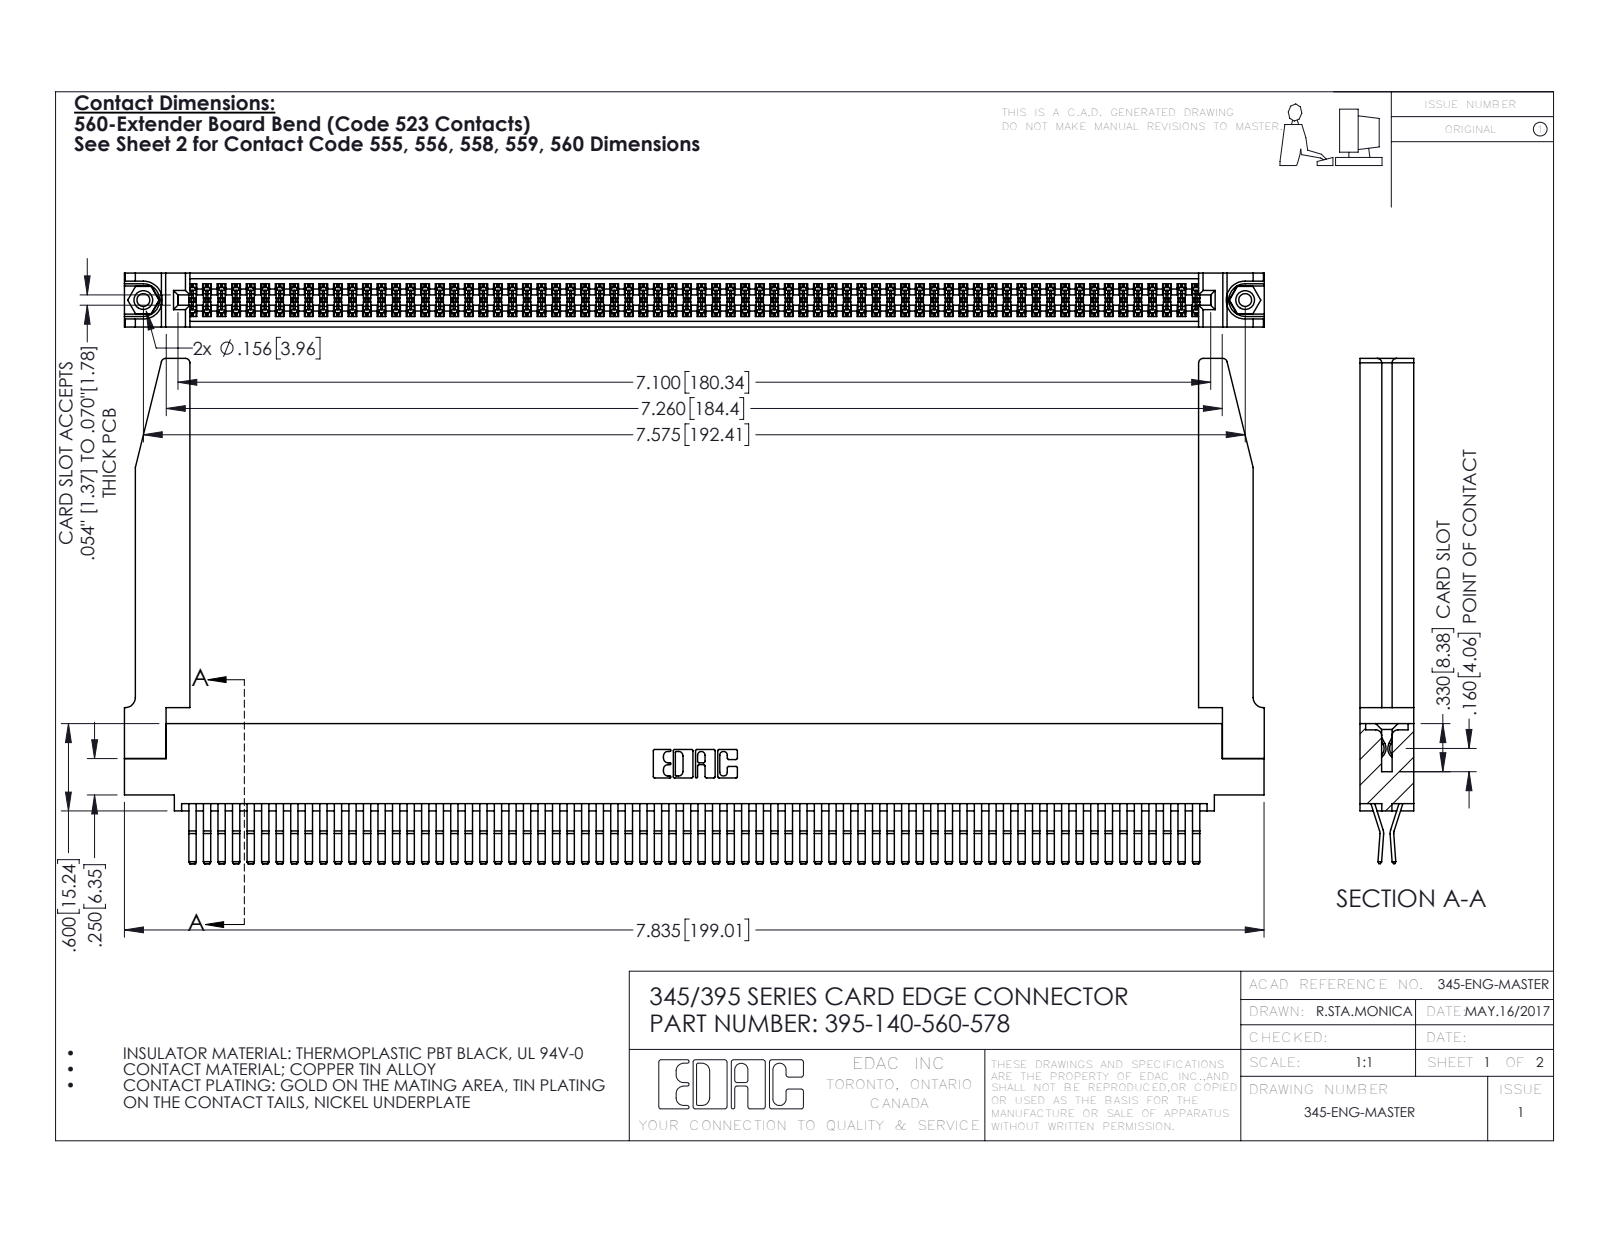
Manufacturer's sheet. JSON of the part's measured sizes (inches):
{"part_name": "345-250-001_345-250-001-102; 395-140-560-578; 345-220-078_345-220-078; 345-292-001_560 Tail (+1 more)", "step_written_by": "SolidWorks 2016 (CONFIG_CONTROL_DESIGN)", "units": "inches", "bodies": {"solids": 145, "faces": 7644, "planar": 4846, "cylindrical": 2746, "other": 52}, "overall_size": [7.836, 3.472, 0.37], "volume_in3": 1.721, "surface_area_in2": 62.07, "round_holes": [[0.089, 2], [0.125, 2], [0.156, 2], [0.064, 1]], "round_bosses_or_shafts": [[0.155, 2]], "partial_cylinders_radius": [[0.006, 210], [0.01, 22], [0.03, 8], [0.007, 6], [0.031, 6], [0.026, 3], [0.01, 2], [0.014, 2]], "face_to_face_distances": [0.072, 0.025, 0.298, 0.37, 0.2, 0.098, 0.272, 0.225, 0.175, 0.149], "hole_center_spacings": [0.27, 7.339, 7.575]}
